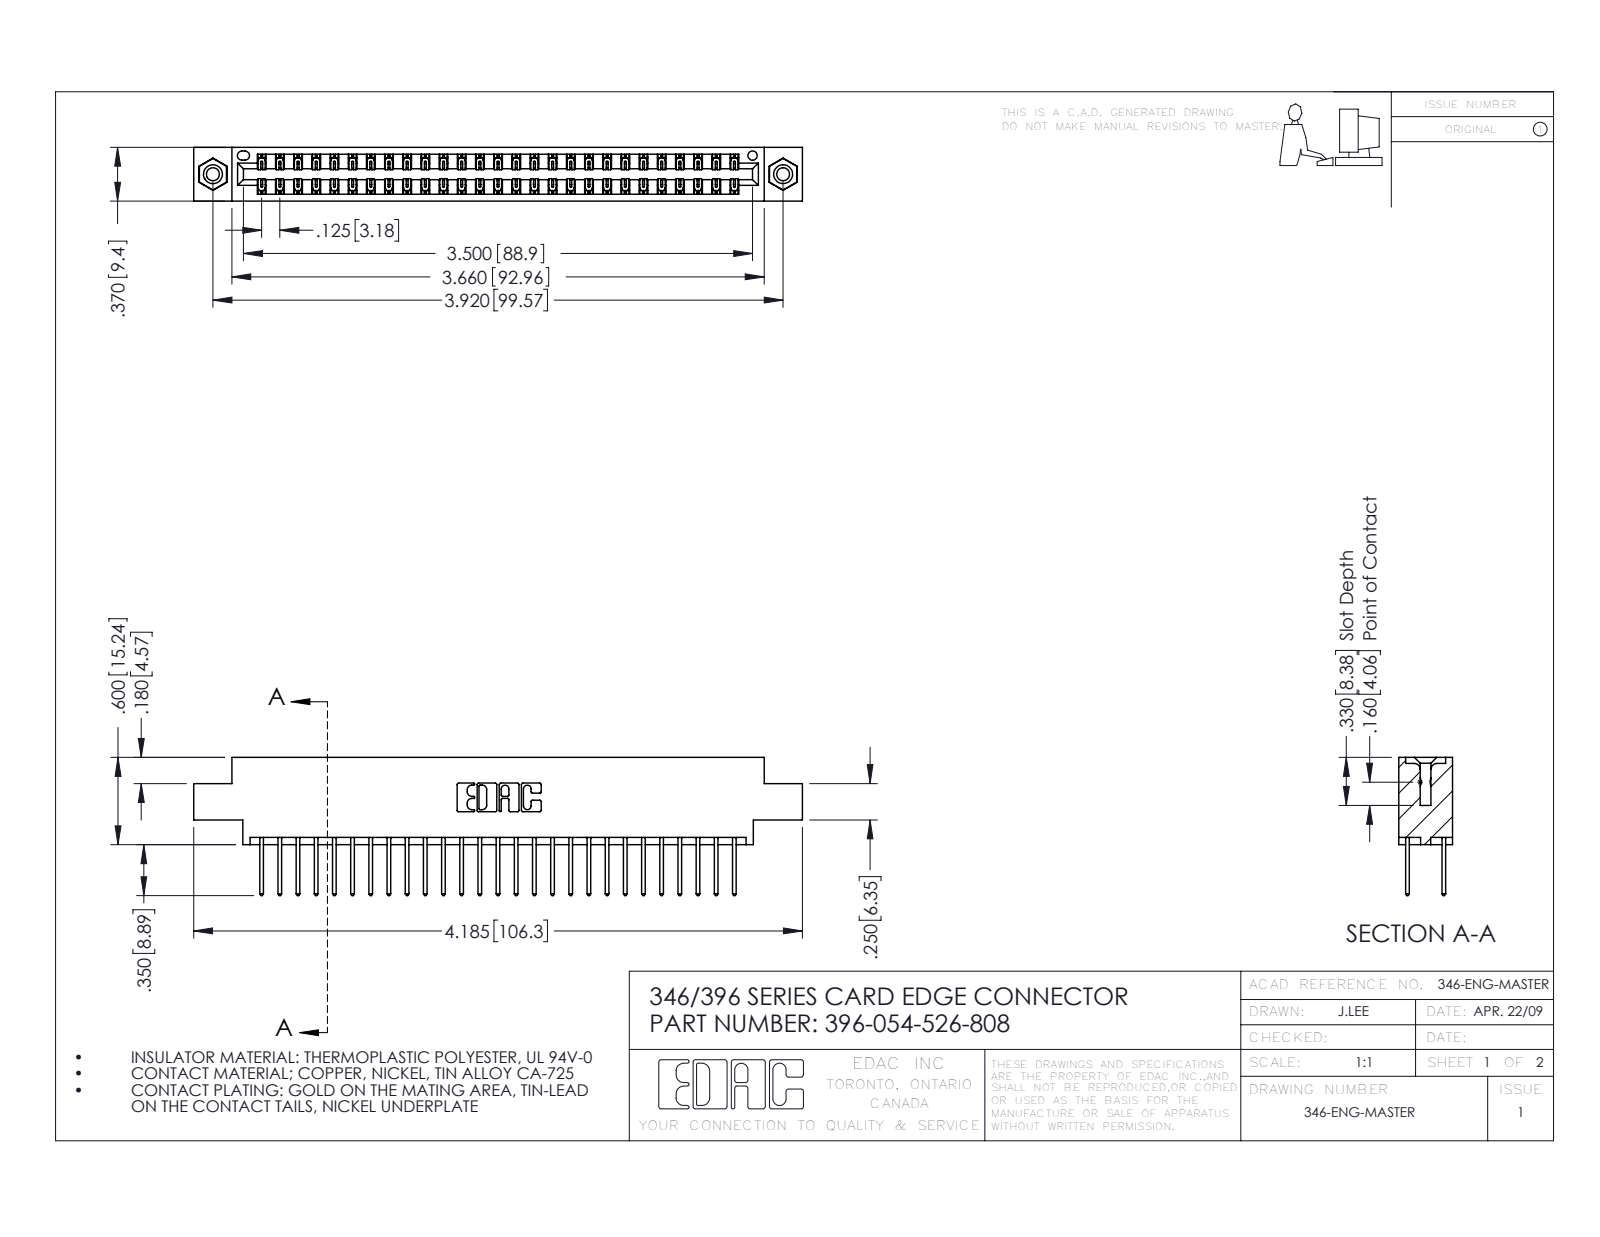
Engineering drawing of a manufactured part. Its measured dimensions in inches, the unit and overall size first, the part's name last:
Units: inches
Overall size (bounding box): 4.185 × 0.95 × 0.37
Round holes (diameter × count): ⌀0.089 ×2, ⌀0.125 ×2, ⌀0.156 ×2, ⌀0.064 ×1
Round bosses / shafts (diameter × count): ⌀0.155 ×2
Partial cylindrical surfaces — rounded edges, fillets, slot ends (radius × count): R0.006 ×81, R0.01 ×54, R0.01 ×22, R0.007 ×6, R0.031 ×6, R0.026 ×3, R0.014 ×2, R0.022 ×2
Main face-to-face distances: 0.048, 0.322, 0.25, 0.37, 0.072, 0.298, 0.025, 0.275, 0.222, 0.148
Hole centre spacings: 0.246, 3.712, 3.92
Volume: 0.621 in³ · Surface area: 22.24 in²
Bodies: 57 solids, 2994 faces (2002 planar, 976 cylindrical, 16 other)
Part name (STEP PRODUCT): 396-054-526-808; 345-250-001_345-250-003-102; 346 Part_0.170 Offset - 0.156 Dia-TI; 345-292-001_345-293-126
STEP written by: SolidWorks 2016 (CONFIG_CONTROL_DESIGN)
